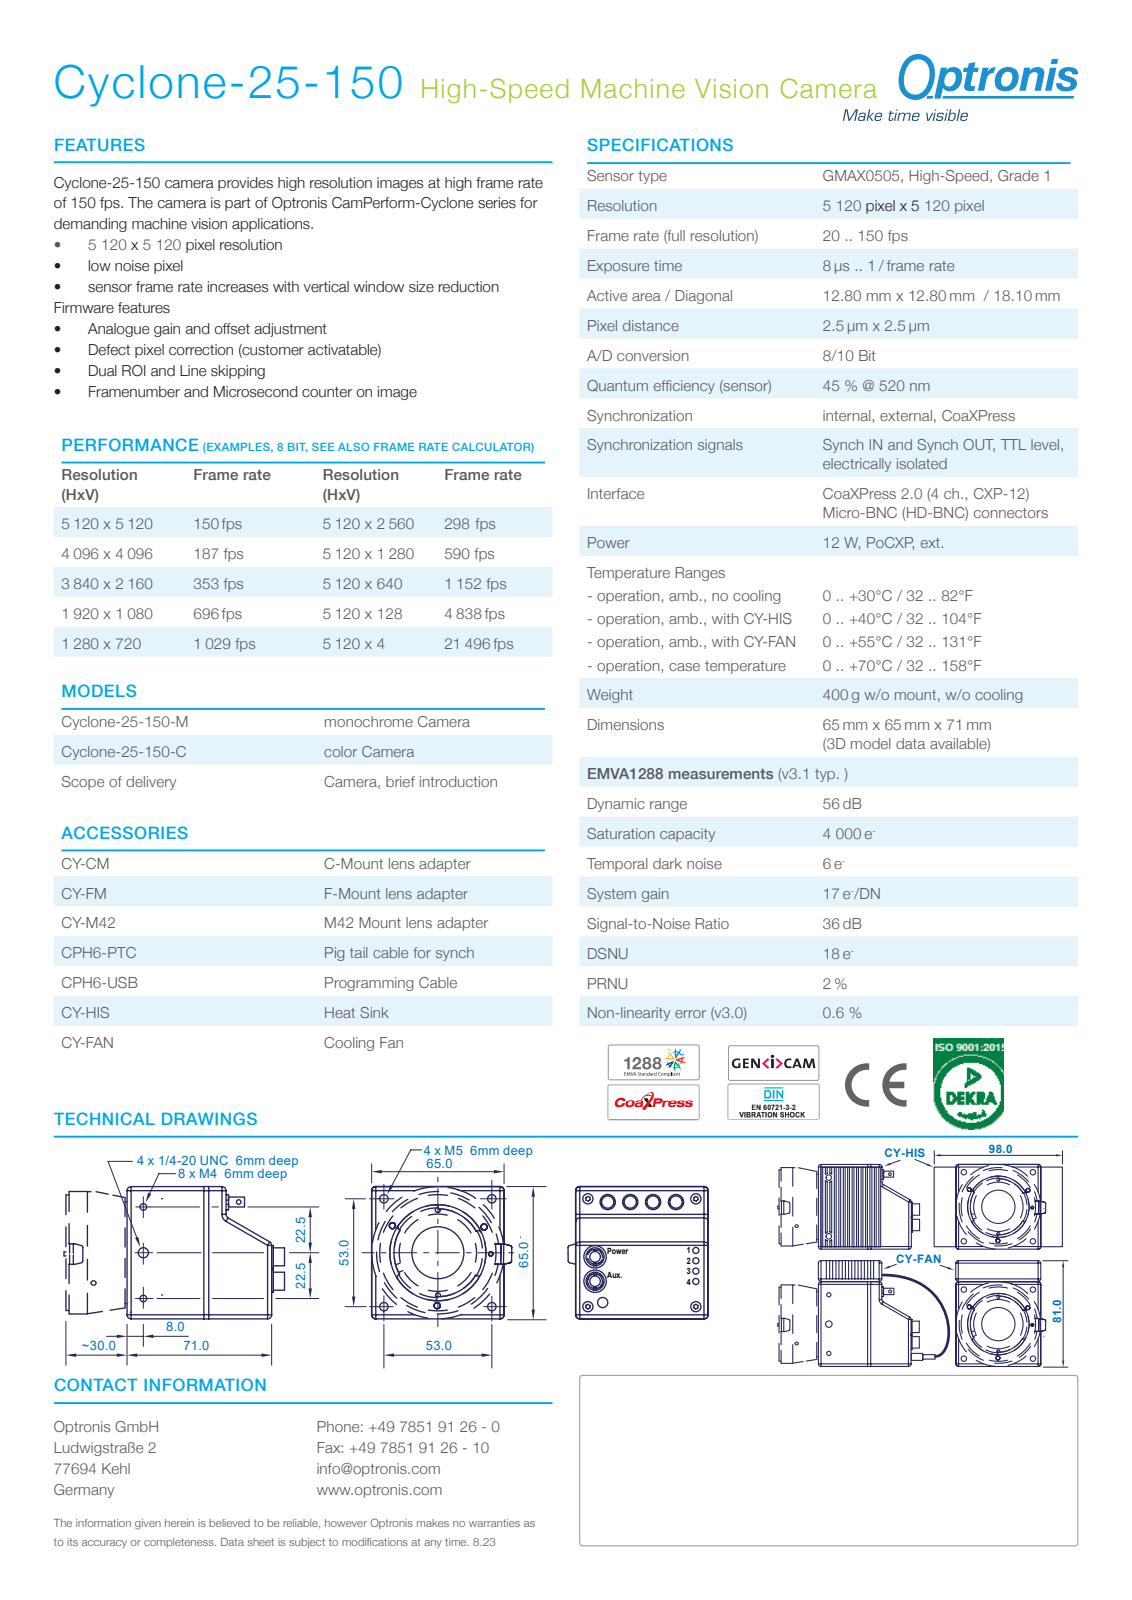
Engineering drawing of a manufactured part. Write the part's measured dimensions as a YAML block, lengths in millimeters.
part_name: "1200-MG-01-D_Cyclone"
step_written_by: "Autodesk Inventor 2026 (AUTOMOTIVE_DESIGN)"
units: millimeters
bodies: {solids: 7, faces: 2556, planar: 1320, cylindrical: 721, other: 515}
overall_size: [77.3, 65.02, 65]
volume: 85827
surface_area: 67426
round_holes:
  - {diameter: 0.8, count: 18}
  - {diameter: 0.5, count: 10}
  - {diameter: 1.57, count: 8}
  - {diameter: 0.45, count: 4}
  - {diameter: 0.46, count: 4}
  - {diameter: 2.7, count: 4}
  - {diameter: 2.8, count: 4}
  - {diameter: 3.05, count: 4}
  - {diameter: 3.24, count: 4}
  - {diameter: 3.59, count: 4}
  - {diameter: 3.6, count: 4}
  - {diameter: 4, count: 4}
round_bosses_or_shafts:
  - {diameter: 1.1, count: 10}
  - {diameter: 7.5, count: 4}
  - {diameter: 6.32, count: 4}
  - {diameter: 5.2, count: 4}
  - {diameter: 4.55, count: 4}
  - {diameter: 4.5, count: 4}
  - {diameter: 3.5, count: 4}
  - {diameter: 3, count: 4}
partial_cylinders:
  - {radius: 3, count: 32}
  - {radius: 1, count: 24}
  - {radius: 2, count: 22}
  - {radius: 0.2, count: 10}
  - {radius: 0.45, count: 10}
  - {radius: 0.16, count: 8}
  - {radius: 0.5, count: 8}
  - {radius: 2.1, count: 4}
face_to_face_distances: [2, 63, 65, 61, 3, 59, 28.4, 0.5, 58.5, 25.4]
hole_center_spacings: [1.8, 3.12, 53, 1.6, 2.26, 11.2, 22.5, 3.6]
